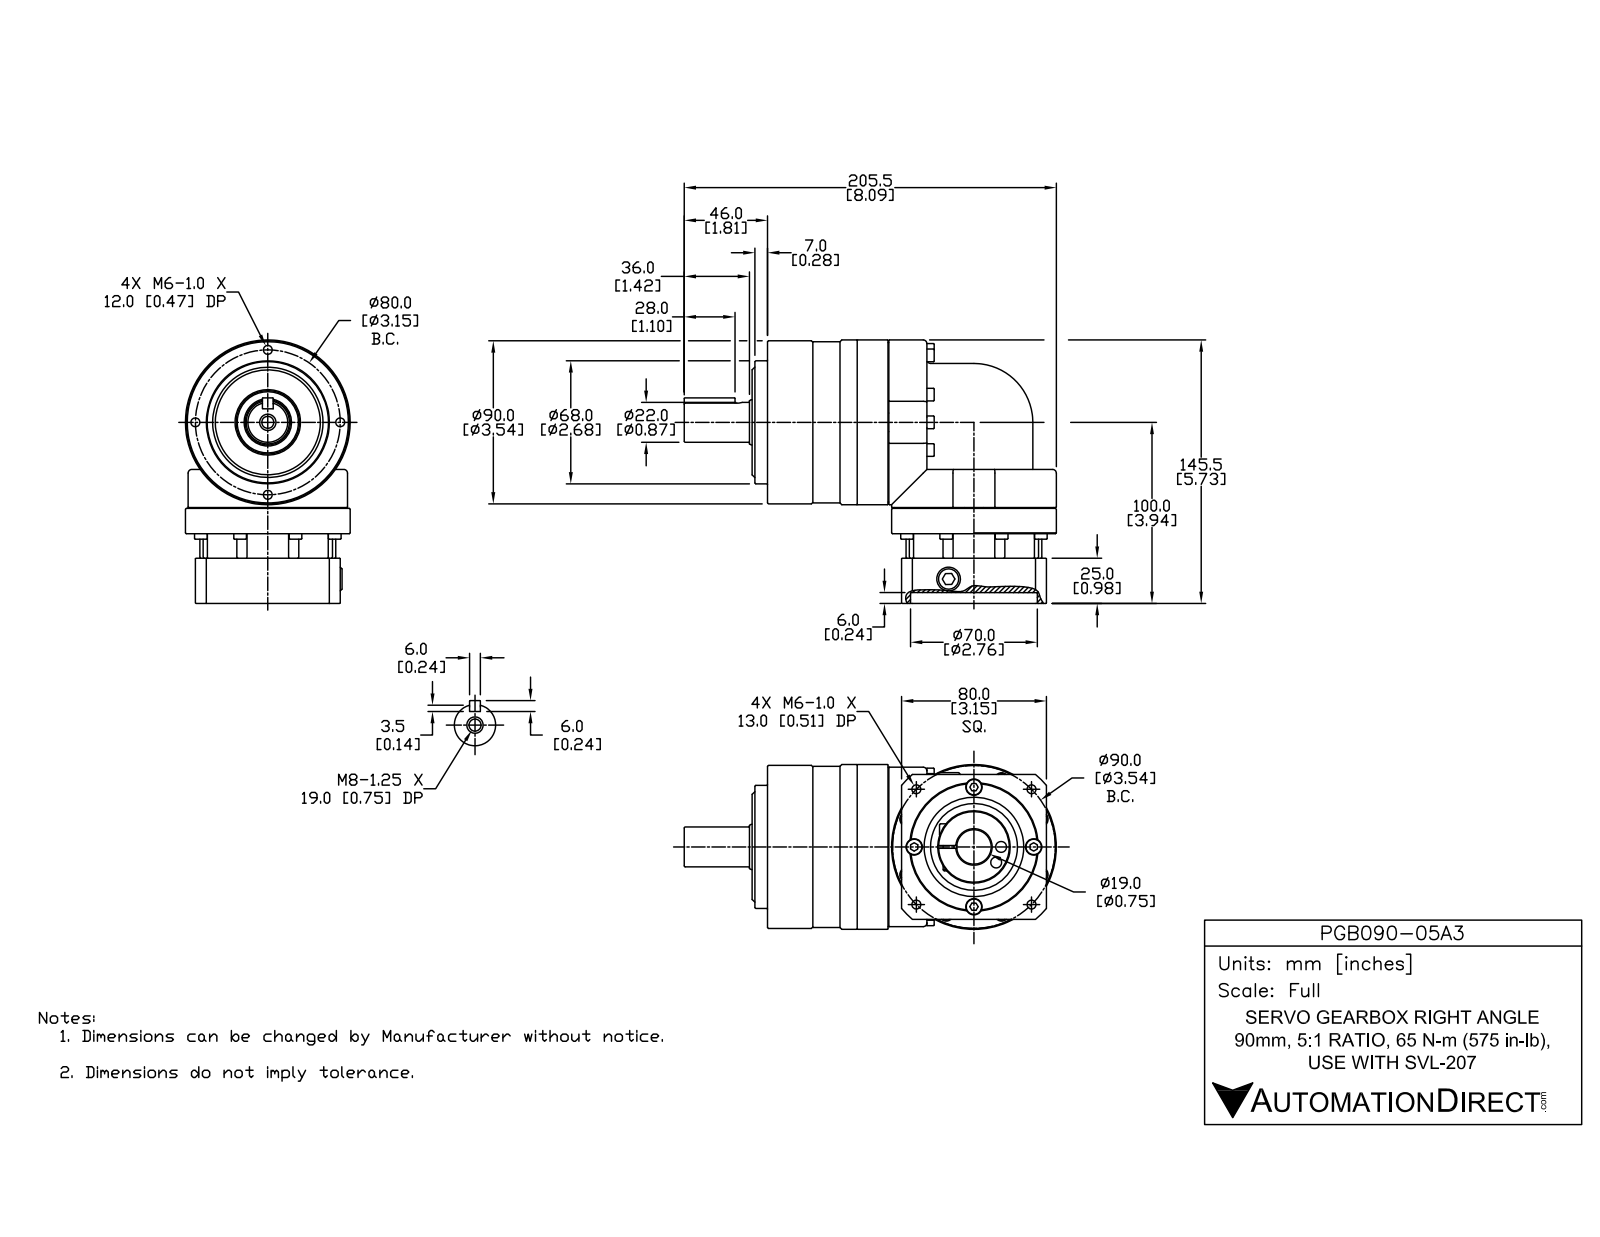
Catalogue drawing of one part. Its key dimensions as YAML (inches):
part_name: "PGB090-05A3"
step_written_by: "SolidWorks 2014 (AUTOMOTIVE_DESIGN)"
units: inches
bodies: {solids: 1, faces: 711, planar: 284, cylindrical: 195, other: 232}
overall_size: [8.091, 5.728, 3.583]
volume: 69.72
surface_area: 153.2
round_holes:
  - {diameter: 0.177, count: 8}
  - {diameter: 0.194, count: 8}
  - {diameter: 0.315, count: 8}
  - {diameter: 0.354, count: 4}
  - {diameter: 0.236, count: 2}
  - {diameter: 0.256, count: 1}
  - {diameter: 0.262, count: 1}
  - {diameter: 0.413, count: 1}
  - {diameter: 0.748, count: 1}
  - {diameter: 1.89, count: 1}
  - {diameter: 2.165, count: 1}
  - {diameter: 2.756, count: 1}
round_bosses_or_shafts:
  - {diameter: 0.276, count: 17}
  - {diameter: 0.157, count: 8}
  - {diameter: 0.335, count: 4}
  - {diameter: 3.583, count: 2}
  - {diameter: 3.465, count: 2}
  - {diameter: 3.543, count: 1}
  - {diameter: 3.504, count: 1}
  - {diameter: 2.953, count: 1}
partial_cylinders:
  - {radius: 0.079, count: 6}
  - {radius: 1.28, count: 2}
  - {radius: 0.097, count: 1}
  - {radius: 0.118, count: 1}
  - {radius: 0.217, count: 1}
  - {radius: 2.067, count: 1}
face_to_face_distances: [2.913, 3.15, 0.984, 0.157, 0.551, 0.335, 0.236, 3.465, 1.398, 0.748]
hole_center_spacings: [0.622, 0.681, 1.206, 1.254, 1.575, 1.613, 1.867, 2.228]
